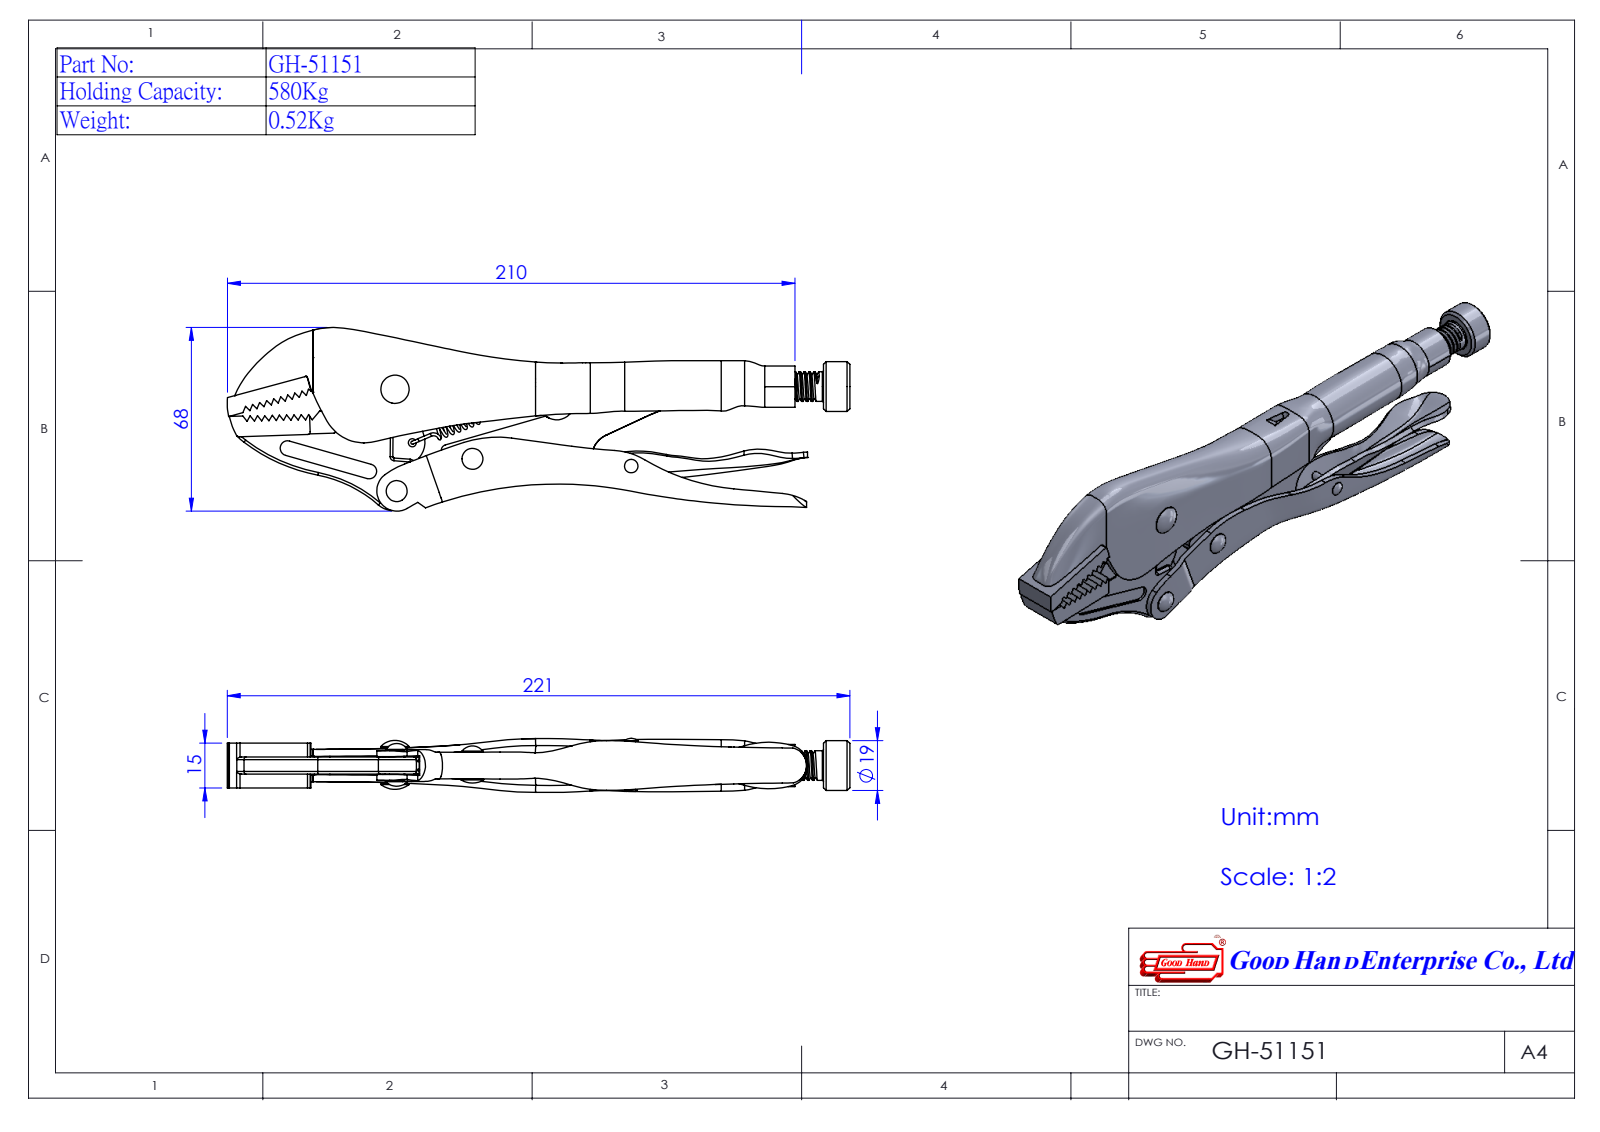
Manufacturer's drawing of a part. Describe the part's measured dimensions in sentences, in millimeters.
The part is named "GH-51151(簡化); Group1^GH-51151(簡化)". Its 3-D file was written by "SolidWorks 2016 (AUTOMOTIVE_DESIGN)". It is 13 solids with 510 faces: 123 planar, 208 cylindrical and 179 other. Overall it measures 231.89 by 68.14 by 20.09 millimeters. Its volume is 73 137 cubic millimeters and its surface area 56 406 square millimeters. Round holes: 2 of diameter 5.6, 1 of diameter 3, 1 of diameter 3.3, 1 of diameter 5.57, 1 of diameter 7.5, 1 of diameter 7.6, 1 of diameter 10.67. Round bosses or shafts: 2 of diameter 7.8, 2 of diameter 5.4, 2 of diameter 1.1, 1 of diameter 18.5, 1 of diameter 11, 1 of diameter 10.5, 1 of diameter 8.4, 1 of diameter 8.2. Partial cylindrical surfaces (rounded edges, fillets, slot ends): 17 of radius 1, 4 of radius 0.5, 3 of radius 2, 2 of radius 2.5, 2 of radius 2.75, 2 of radius 8.5, 2 of radius 9.2, 2 of radius 24.58. The main face-to-face distances are 5.5, 0.9, 4.6, 6.4, 5.15, 6.05, 10.65, 11.55, 4.95, 11.75. The hole center spacings are 18.86, 20.87, 23.09, 30.56, 37.8, 38.64, 59, 81.7.
